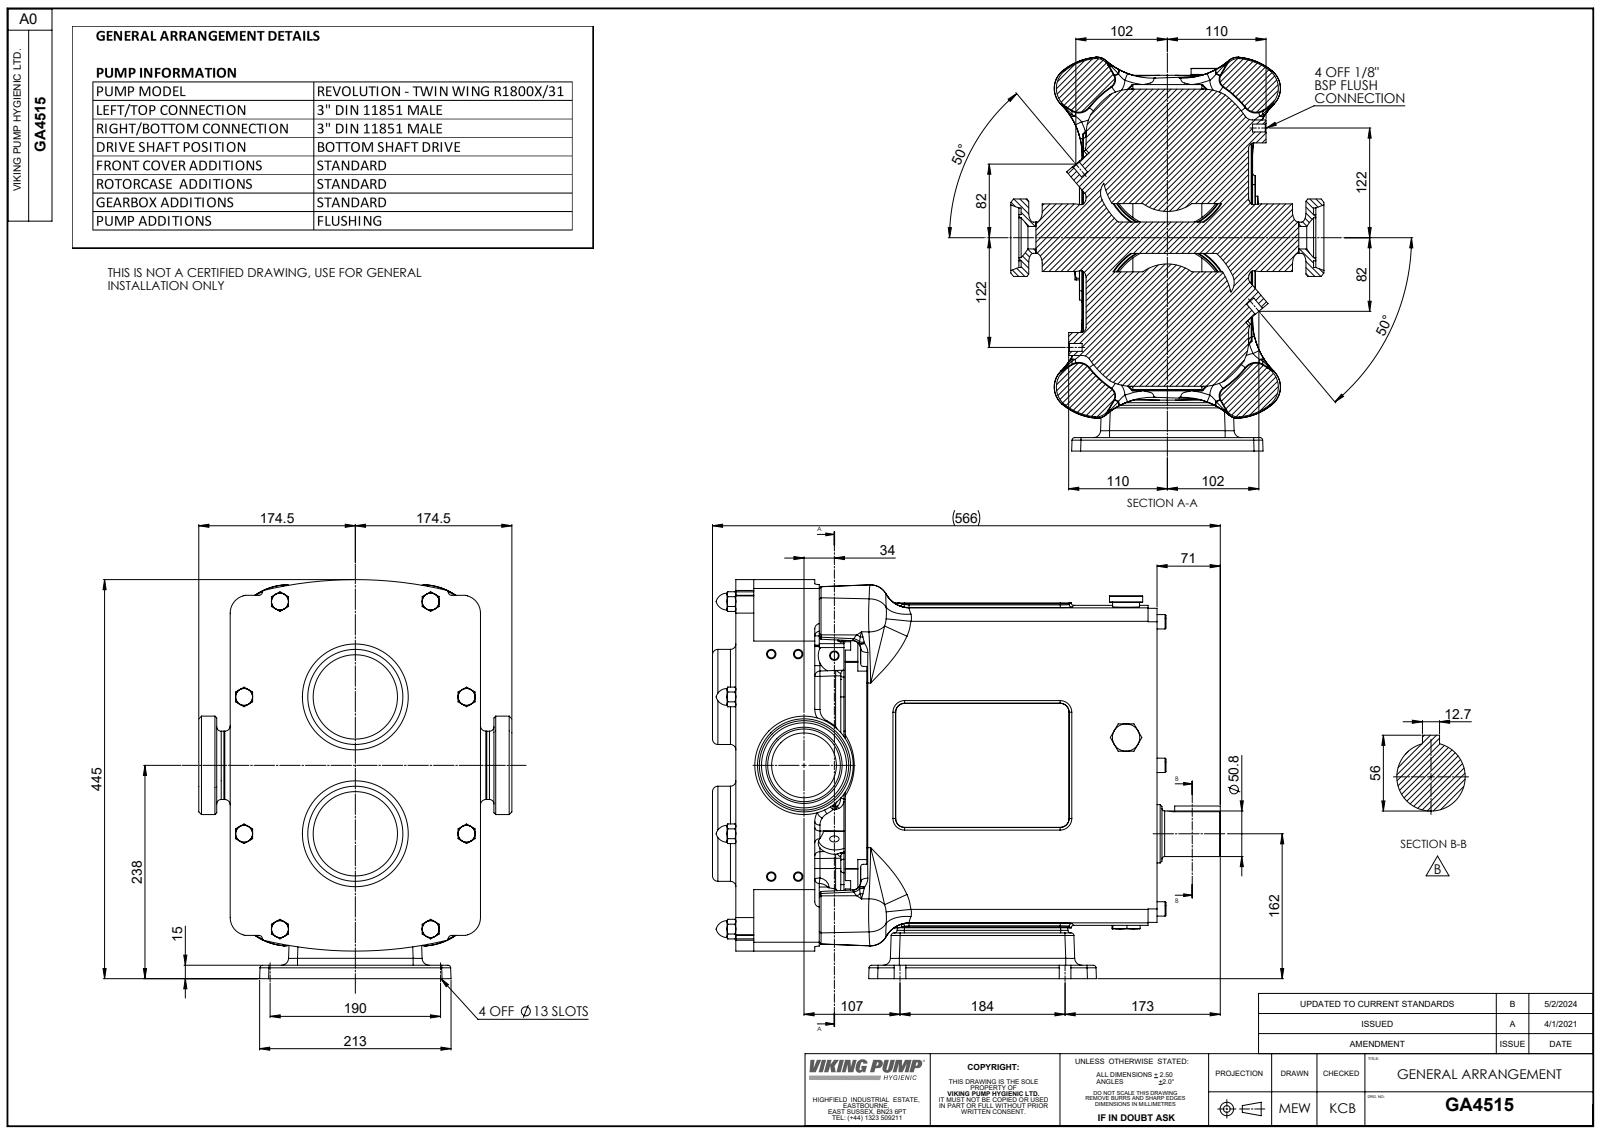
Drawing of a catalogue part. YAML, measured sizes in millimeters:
part_name: "Copy of Z94-5031-55 - 3 INCH DIN11851^GA4515; Copy of R1800 CPP H BSD^GA4515; GA4515"
step_written_by: "SolidWorks 2023 (AUTOMOTIVE_DESIGN)"
units: millimeters
bodies: {solids: 13, faces: 1548, planar: 499, cylindrical: 367, other: 682}
overall_size: [566, 444.75, 349]
volume: 37460000
surface_area: 1211000
round_holes:
  - {diameter: 8.5, count: 4}
  - {diameter: 8.8, count: 3}
  - {diameter: 10.2, count: 1}
  - {diameter: 10.5, count: 1}
  - {diameter: 35, count: 1}
  - {diameter: 72.2, count: 1}
  - {diameter: 81, count: 1}
  - {diameter: 94.8, count: 1}
  - {diameter: 149, count: 1}
round_bosses_or_shafts:
  - {diameter: 16, count: 6}
  - {diameter: 106, count: 2}
  - {diameter: 109.7, count: 1}
  - {diameter: 94, count: 1}
  - {diameter: 85, count: 1}
  - {diameter: 76.2, count: 1}
  - {diameter: 76.1, count: 1}
  - {diameter: 65, count: 1}
partial_cylinders:
  - {radius: 3, count: 44}
  - {radius: 6, count: 36}
  - {radius: 10, count: 30}
  - {radius: 5, count: 16}
  - {radius: 4, count: 14}
  - {radius: 8, count: 10}
  - {radius: 15, count: 8}
  - {radius: 0.74, count: 6}
face_to_face_distances: [190, 469.5, 3, 193, 41.5, 44.5, 234.5, 237.5, 323.5, 146]
hole_center_spacings: [30, 40.39, 70.37, 124.17, 126.85, 129.26, 248, 249.53]
